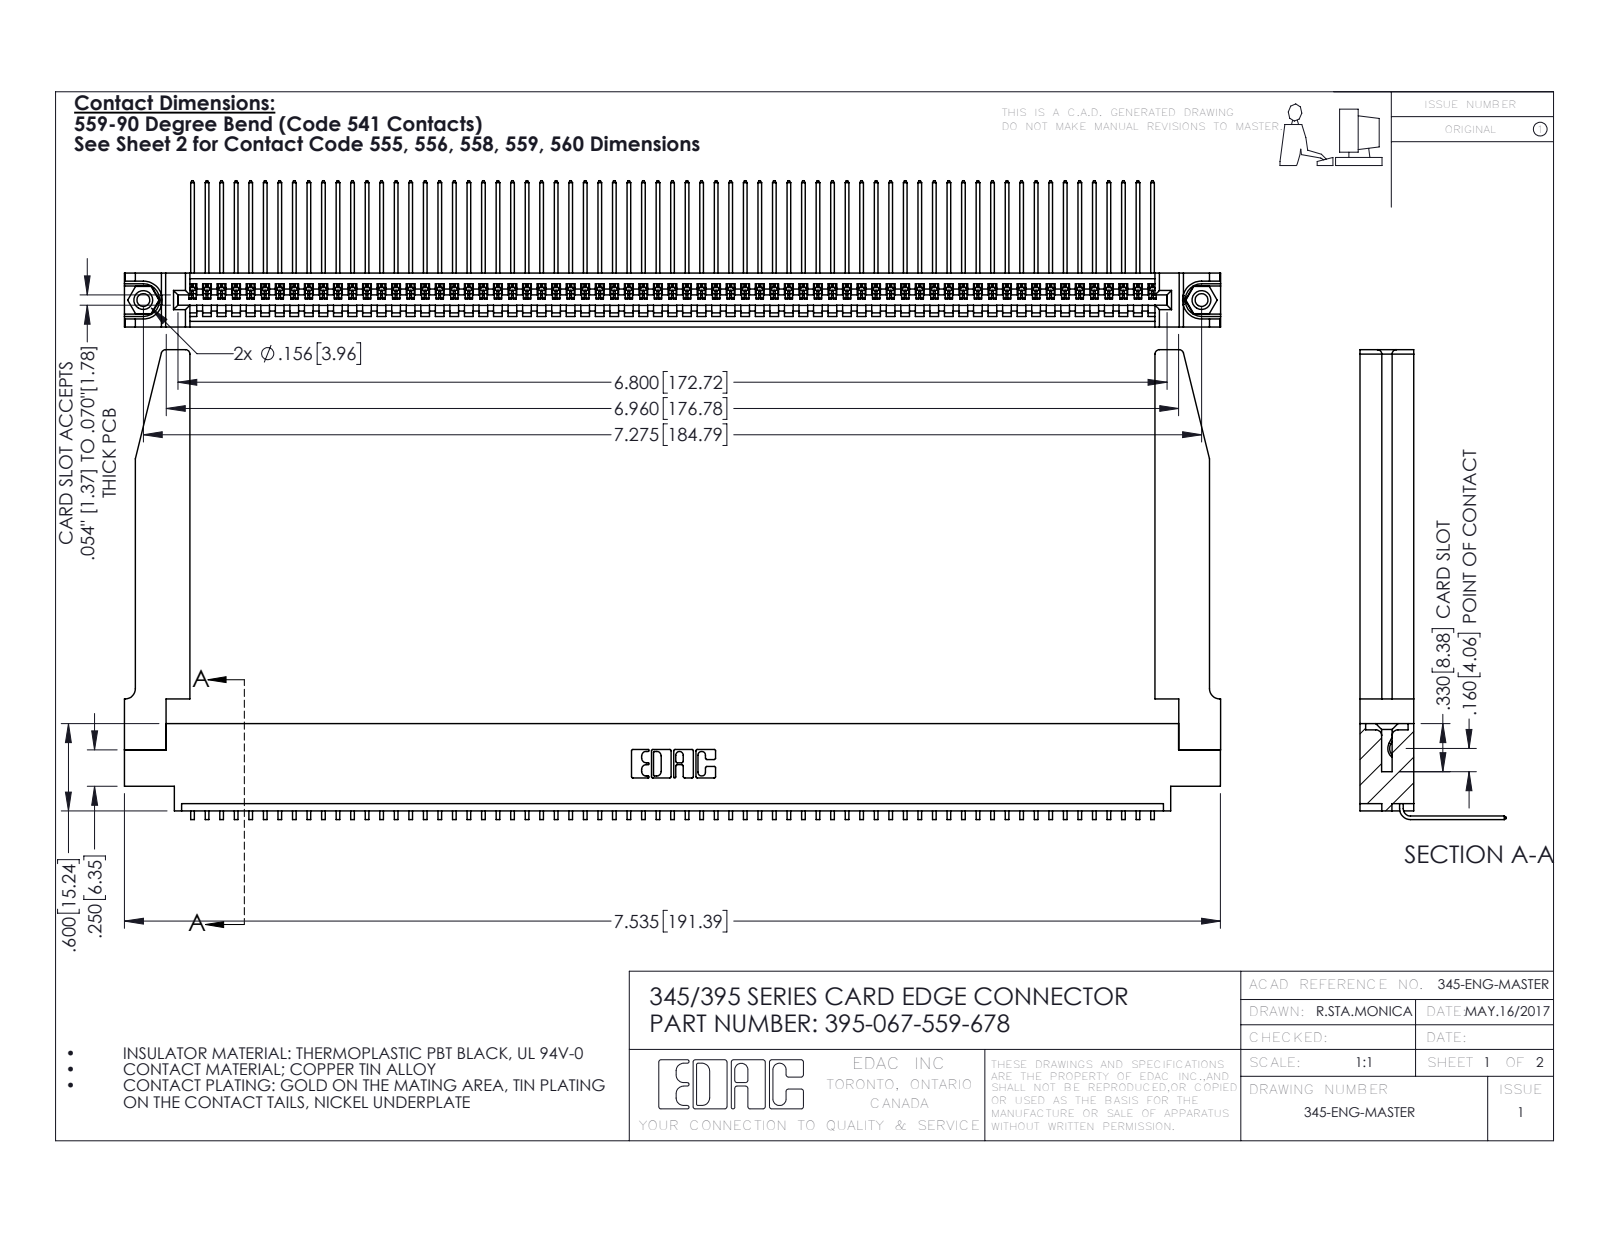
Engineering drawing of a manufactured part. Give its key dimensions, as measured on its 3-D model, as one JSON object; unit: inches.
{"part_name": "395-067-559-678; 345-250-001_345-250-001-102; 345 Part_0.170 Offset - 0.156 Dia-TH; 345-220-078_345-220-078 (+1 more)", "step_written_by": "SolidWorks 2016 (CONFIG_CONTROL_DESIGN)", "units": "inches", "bodies": {"solids": 72, "faces": 4384, "planar": 3040, "cylindrical": 1292, "other": 52}, "overall_size": [7.536, 3.229, 1.005], "volume_in3": 1.603, "surface_area_in2": 51.46, "round_holes": [[0.089, 2], [0.125, 2], [0.156, 2], [0.064, 1]], "round_bosses_or_shafts": [[0.155, 2]], "partial_cylinders_radius": [[0.006, 134], [0.01, 22], [0.03, 8], [0.007, 6], [0.031, 6], [0.026, 3], [0.031, 2], [0.04, 2]], "face_to_face_distances": [0.37, 0.072, 0.298, 0.098, 0.272, 0.025, 0.2, 0.225, 0.175, 0.149], "hole_center_spacings": [0.27, 7.039, 7.275]}
